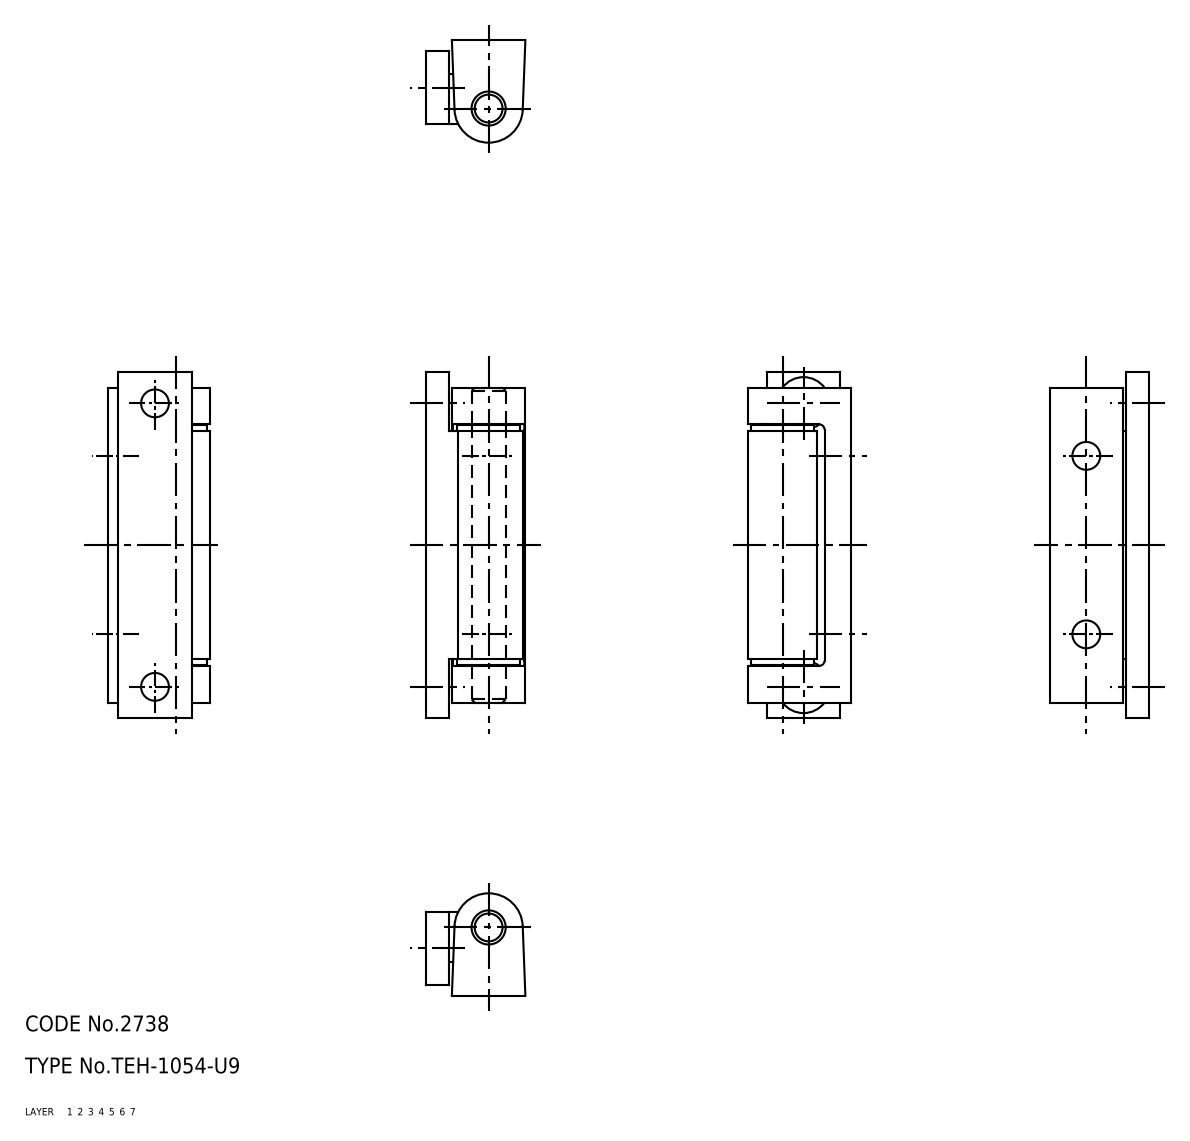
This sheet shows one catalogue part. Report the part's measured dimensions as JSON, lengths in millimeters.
{"part_name": "bushing; shaft; hinge pieces_B; hinge pieces_A (+1 more)", "step_written_by": "CADfix (AUTOMOTIVE_DESIGN)", "units": "millimeters", "bodies": {"solids": 5, "faces": 76, "planar": 0, "cylindrical": 0, "other": 76}, "overall_size": [66, 19.5, 19], "volume_mm3": 16298, "surface_area_mm2": 10827}
